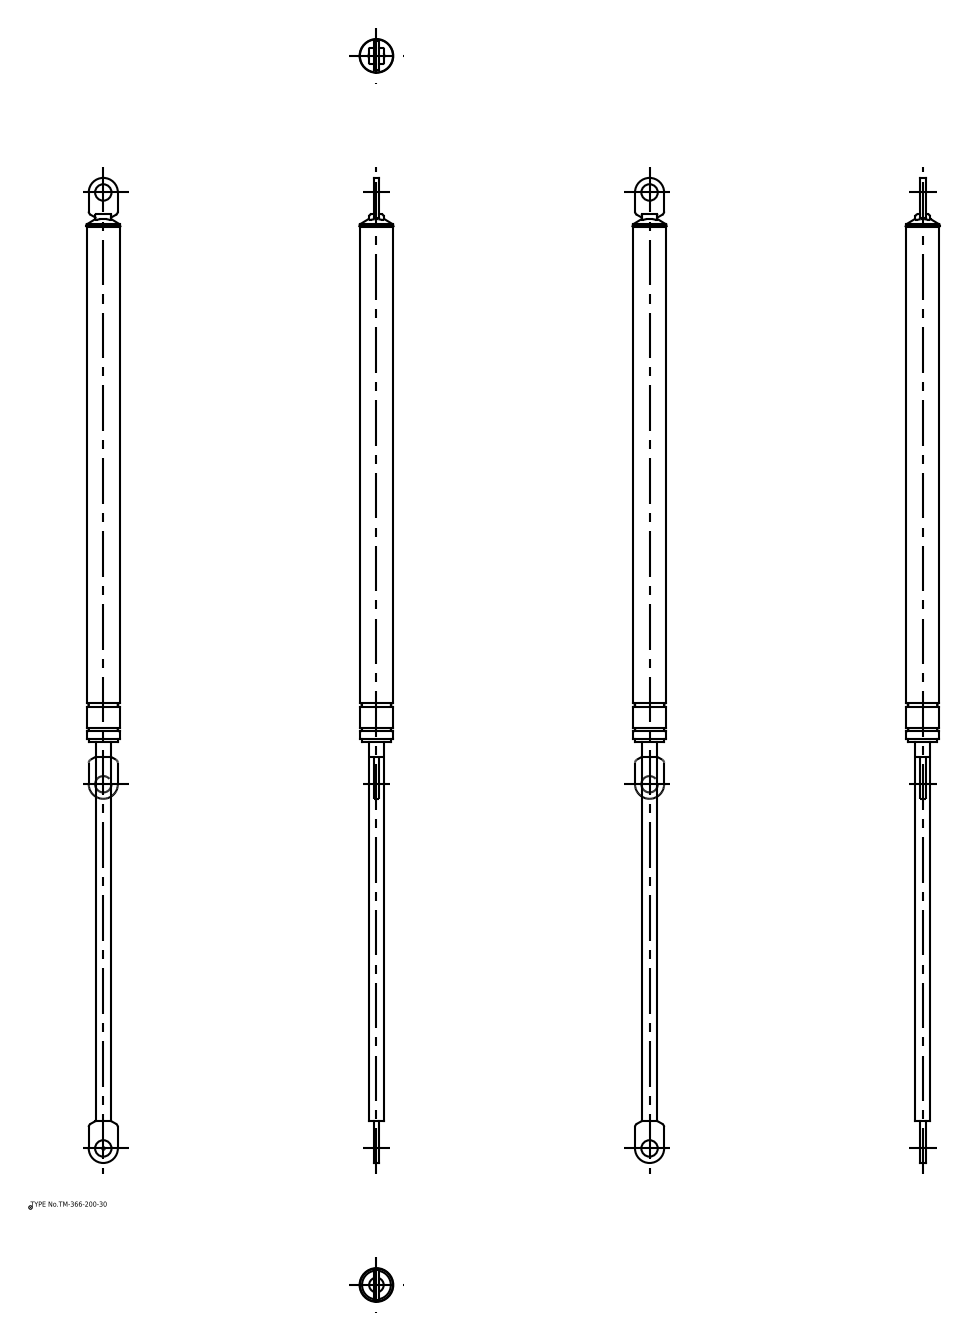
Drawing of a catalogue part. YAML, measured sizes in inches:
part_name: "TM_366_200_30; TM_366_200_30_div"
step_written_by: "spGate 16.7.1 (AUTOMOTIVE_DESIGN)"
units: inches
bodies: {solids: 2, faces: 89, planar: 35, cylindrical: 36, other: 18}
overall_size: [21.299, 0.728, 0.728]
volume: 5.175
surface_area: 36.7
round_holes:
  - {diameter: 0.354, count: 2}
round_bosses_or_shafts:
  - {diameter: 0.709, count: 1}
  - {diameter: 0.622, count: 1}
  - {diameter: 0.315, count: 1}
partial_cylinders:
  - {radius: 0.012, count: 8}
  - {radius: 0.079, count: 4}
  - {radius: 0.02, count: 2}
  - {radius: 0.045, count: 2}
  - {radius: 0.315, count: 2}
face_to_face_distances: [0.126, 0.63, 0.067, 8.189, 8.256, 0.146, 0.484, 0.531, 0.071, 0.094]
hole_center_spacings: [20.669]
